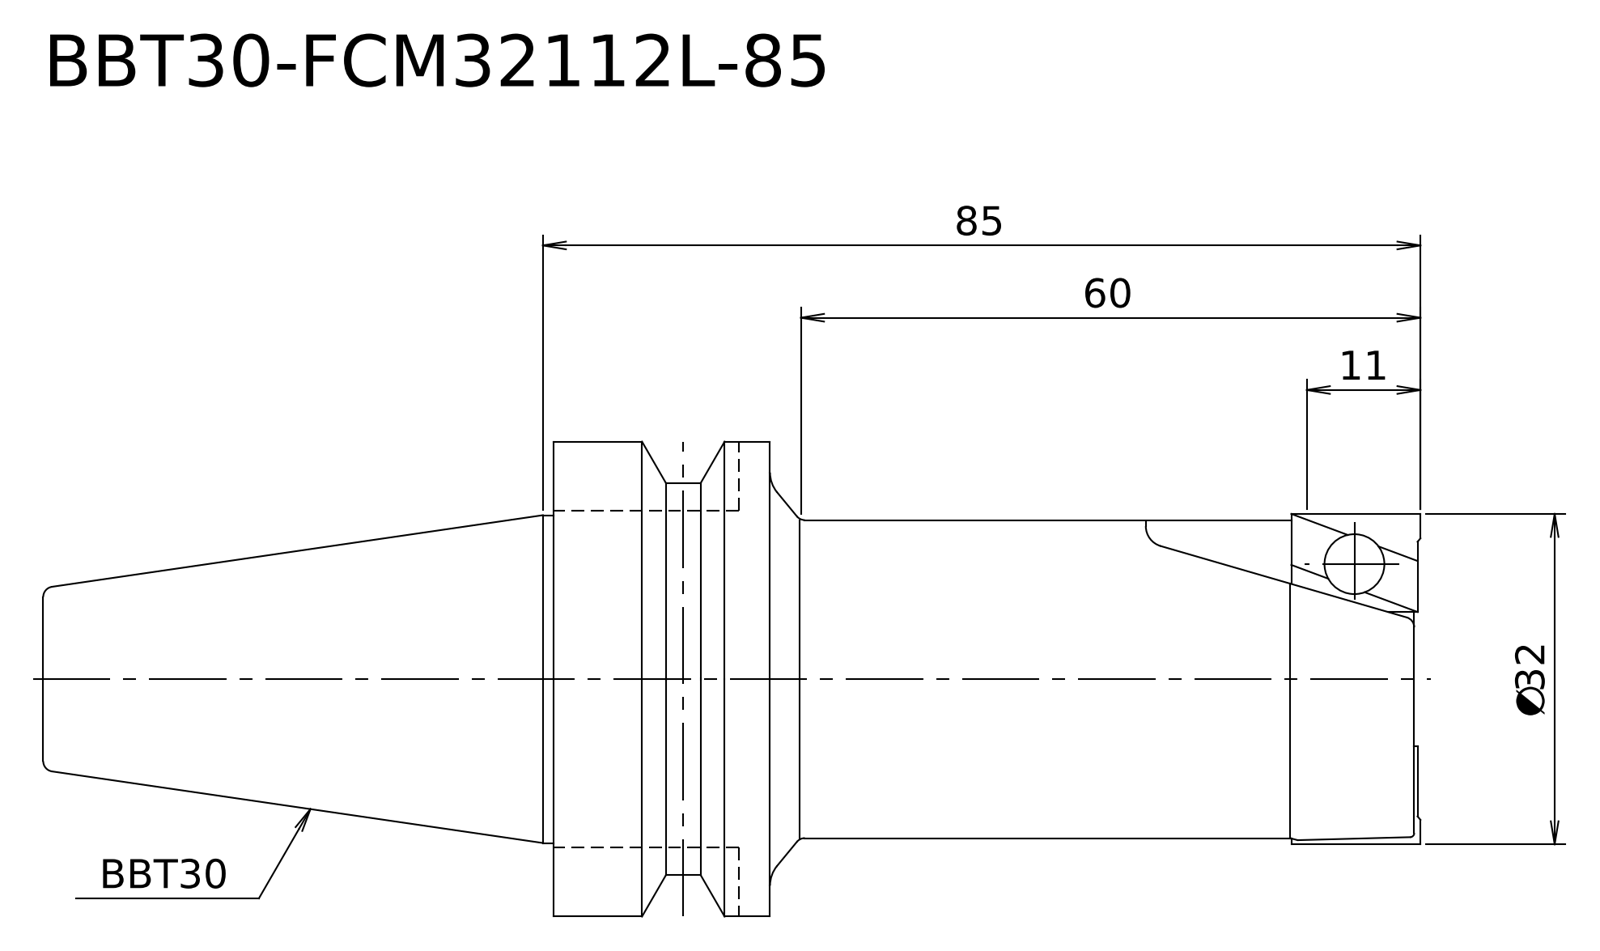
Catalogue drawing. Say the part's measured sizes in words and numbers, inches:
Its 3-D file was written by "Kubotek KeyCreator V8.5.1 (14335) (CONFIG_CONTROL_DESIGN)". It is 1 solid with 17 faces: 4 planar, 6 cylindrical and 7 other. Overall it measures 5.252 by 1.811 by 1.811 inches. Its volume is 6.388 cubic inches and its surface area 25.09 square inches. Round bosses or shafts: 1 of diameter 1.811, 1 of diameter 1.496, 1 of diameter 1.26, 1 of diameter 1.25, 1 of diameter 1.213. The main face-to-face distances are 3.307, 2.48, 0.827, 5.252, 2.772, 1.945.
